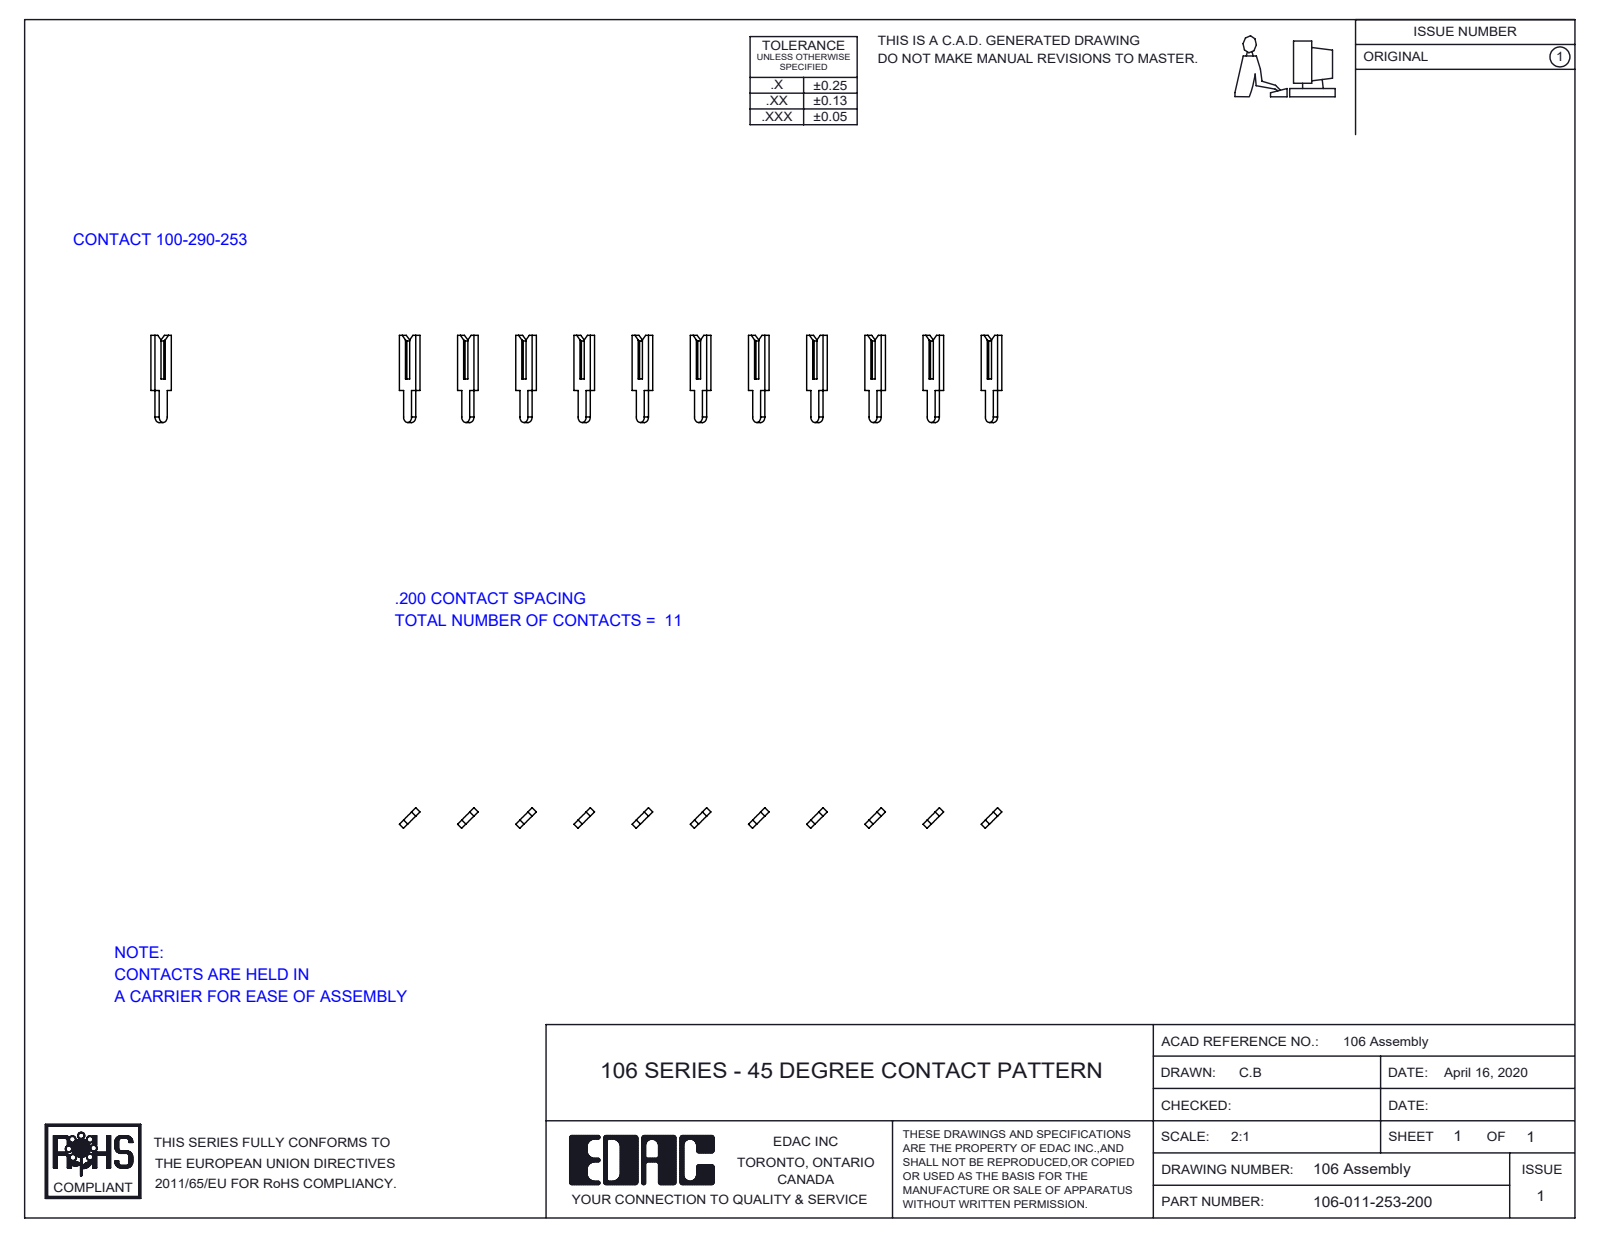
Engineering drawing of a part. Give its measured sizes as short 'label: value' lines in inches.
name: 106-011-253-200; 100-290-001_100-290-253
written by: SolidWorks 2016 (CONFIG_CONTROL_DESIGN)
unit: in
bodies: 11 solids, 220 faces (209 planar, 11 cylindrical, 0 other)
size: 2.071 × 0.3 × 0.071
volume: 0.004 in³; area: 0.587 in²
rounds: 11× R0.019
face distances: 0.141, 0.283, 0.566, 0.707, 0.848, 0.424, 0.424, 0.283, 0.161, 0.303
